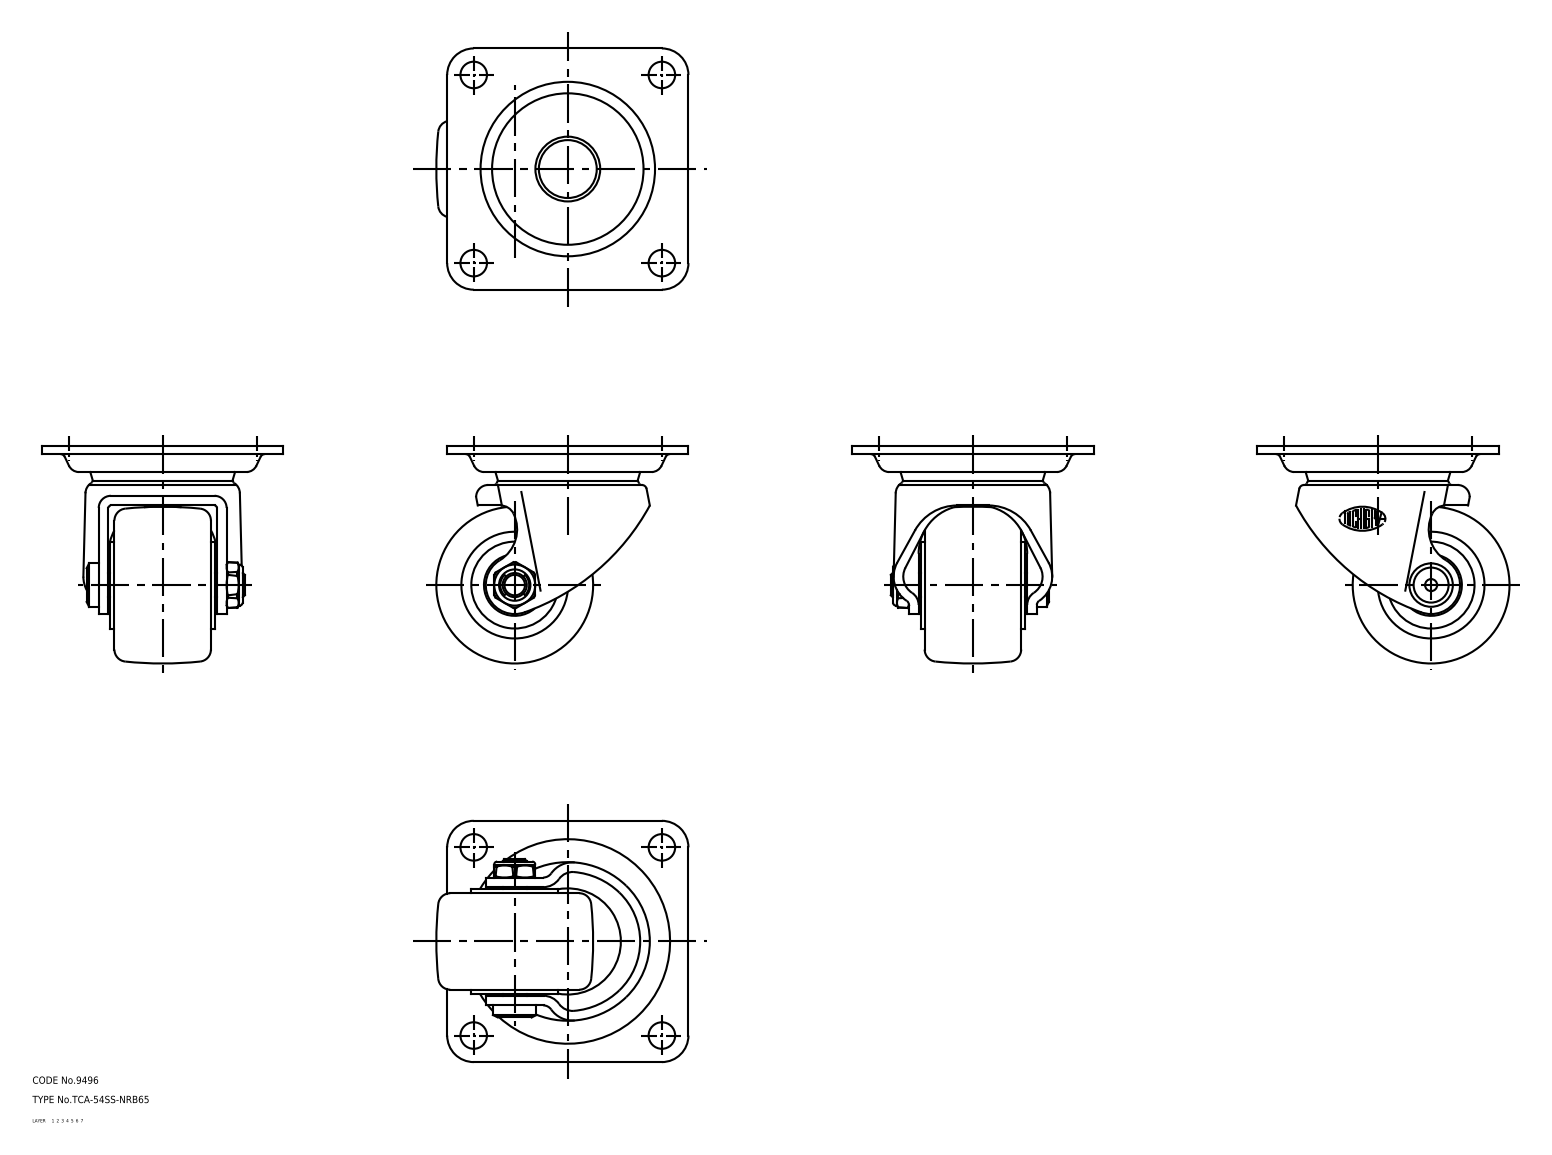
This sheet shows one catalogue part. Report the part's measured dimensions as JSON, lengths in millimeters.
{"part_name": "nut; seal; main shaft; wheel (+3 more)", "step_written_by": "CADfix (AUTOMOTIVE_DESIGN)", "units": "millimeters", "bodies": {"solids": 7, "faces": 226, "planar": 0, "cylindrical": 0, "other": 226}, "overall_size": [104.5, 100, 90], "volume_mm3": 237571, "surface_area_mm2": 69994}
